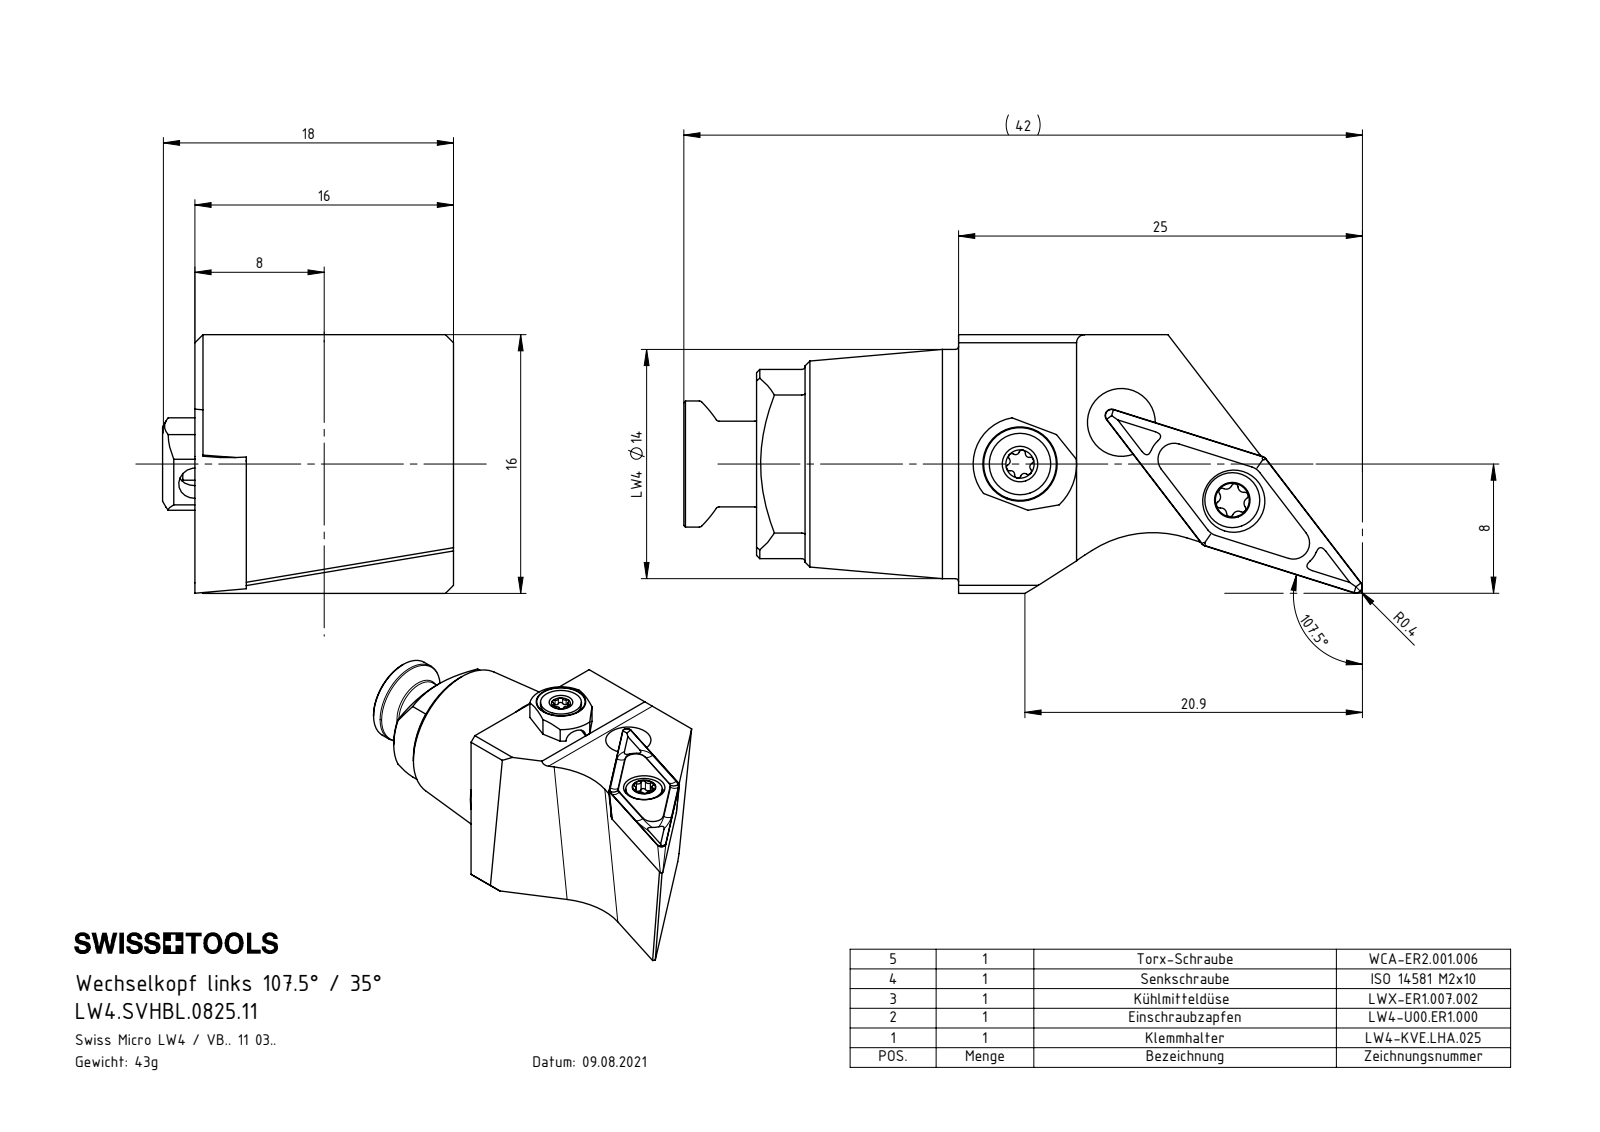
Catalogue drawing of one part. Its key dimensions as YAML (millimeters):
part_name: "LW4.SVHBL.0825.11; VBMT110304; LW4-KVE.LHA.025_A; LWX-ER1.007.004_A (+3 more)"
step_written_by: "SolidWorks 2022 (CONFIG_CONTROL_DESIGN)"
units: millimeters
bodies: {solids: 6, faces: 261, planar: 70, cylindrical: 83, other: 108}
overall_size: [41.69, 19.5, 16]
volume: 5369
surface_area: 3443
round_holes:
  - {diameter: 2, count: 3}
  - {diameter: 1.6, count: 1}
  - {diameter: 2.05, count: 1}
  - {diameter: 2.5, count: 1}
  - {diameter: 2.8, count: 1}
  - {diameter: 3, count: 1}
  - {diameter: 3.85, count: 1}
  - {diameter: 4.2, count: 1}
  - {diameter: 5.5, count: 1}
round_bosses_or_shafts:
  - {diameter: 14.17, count: 1}
  - {diameter: 7.7, count: 1}
  - {diameter: 6, count: 1}
  - {diameter: 5.3, count: 1}
  - {diameter: 5, count: 1}
  - {diameter: 3.8, count: 1}
  - {diameter: 3.4, count: 1}
  - {diameter: 2.5, count: 1}
partial_cylinders:
  - {radius: 0.2, count: 8}
  - {radius: 0.21, count: 6}
  - {radius: 0.24, count: 6}
  - {radius: 0.36, count: 4}
  - {radius: 0.36, count: 2}
  - {radius: 0.5, count: 1}
  - {radius: 2.9, count: 1}
  - {radius: 4.5, count: 1}
face_to_face_distances: [16, 12.82, 3.18, 15.5, 2.68, 0.5, 4, 12.5, 2, 12]
hole_center_spacings: [6.78, 8.38, 8.49, 13.33, 13.43]
